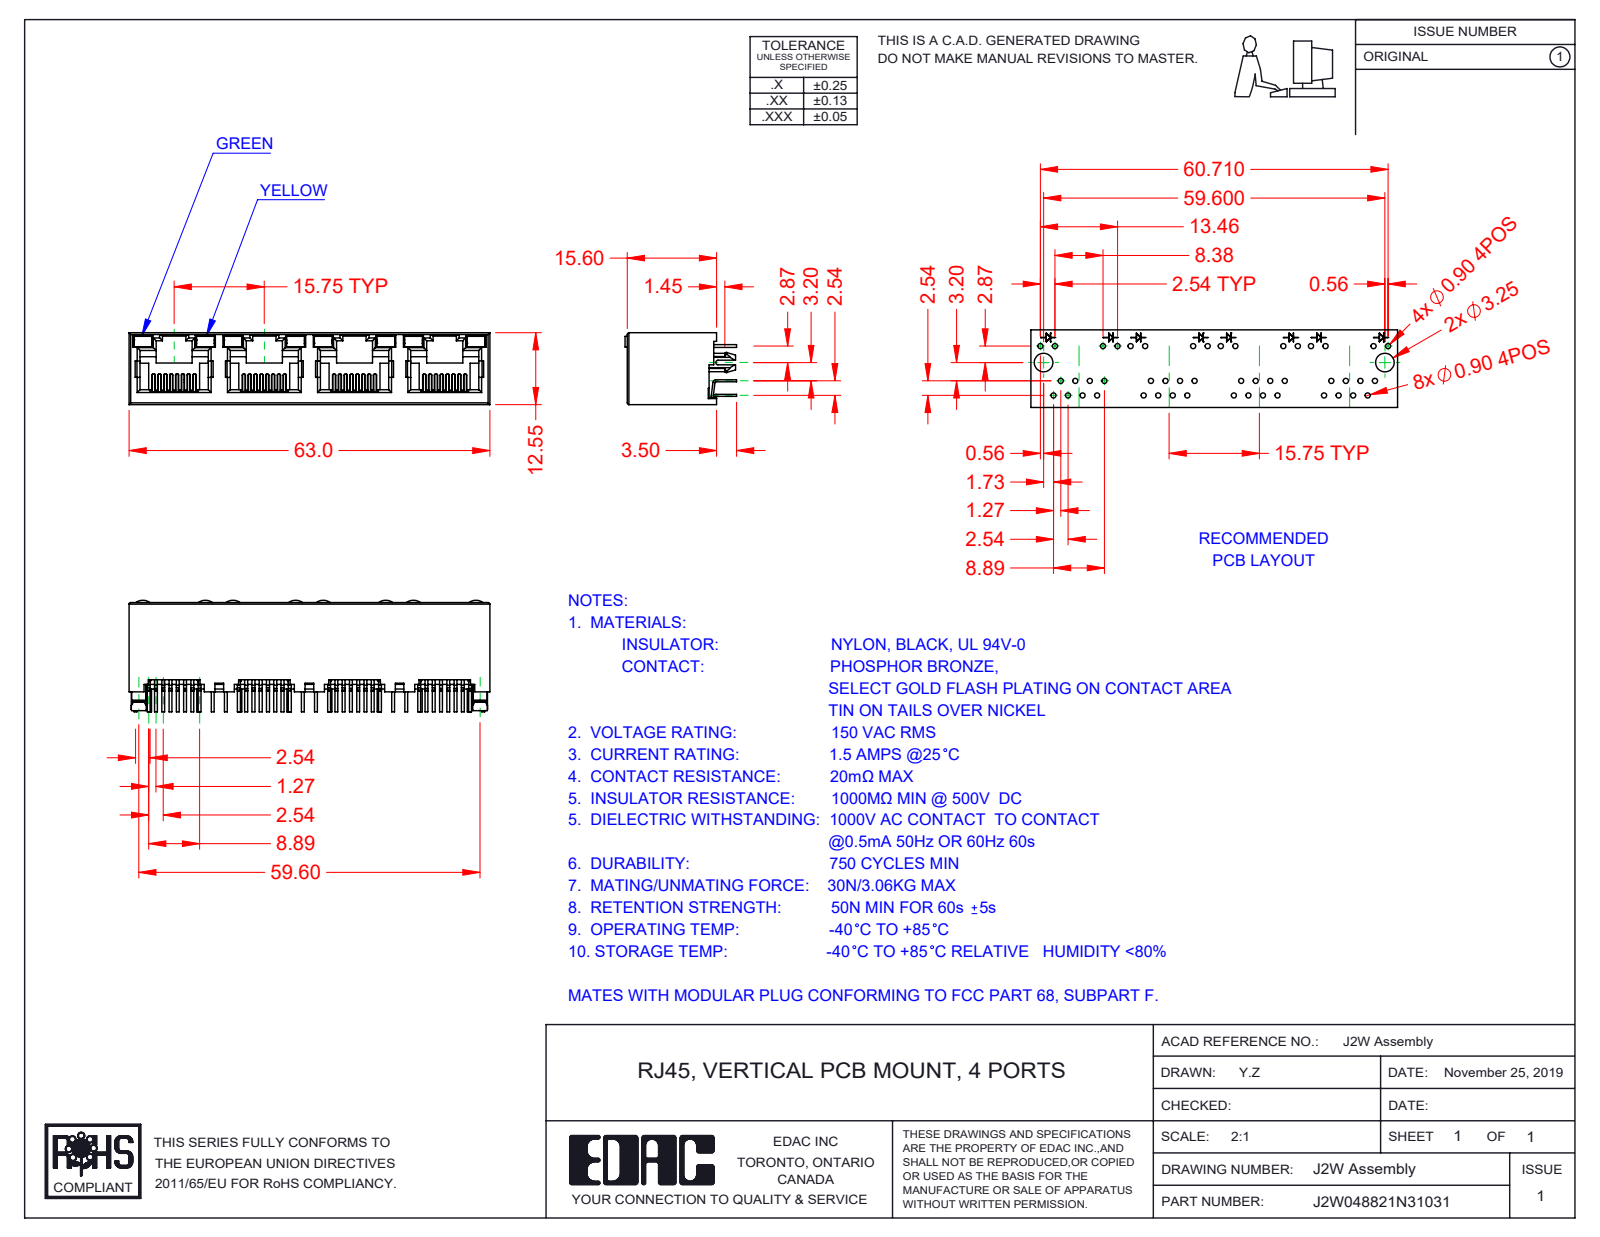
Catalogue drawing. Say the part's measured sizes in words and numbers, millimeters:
The part is named "2W LED RH_1-Yellow; 2W Contacts; 2W Insulator; 2W LED LH_3-Green (+2 more)". Its 3-D file was written by "SolidWorks 2020 (CONFIG_CONTROL_DESIGN)". It is 45 solids with 3135 faces: 2600 planar, 477 cylindrical and 58 other. Overall it measures 63 by 19.5 by 12.55 millimeters. Its volume is 5 335 cubic millimeters and its surface area 13 144 square millimeters. Partial cylindrical surfaces (rounded edges, fillets, slot ends): 64 of radius 0.15, 29 of radius 0.2, 28 of radius 0.5, 14 of radius 0.3, 8 of radius 0.45, 8 of radius 2, 2 of radius 0.25, 2 of radius 1.5. The main face-to-face distances are 12.55, 11.9, 0.65, 15.75, 0.36, 1.5, 0.78, 0.6, 11.3, 31.5.
